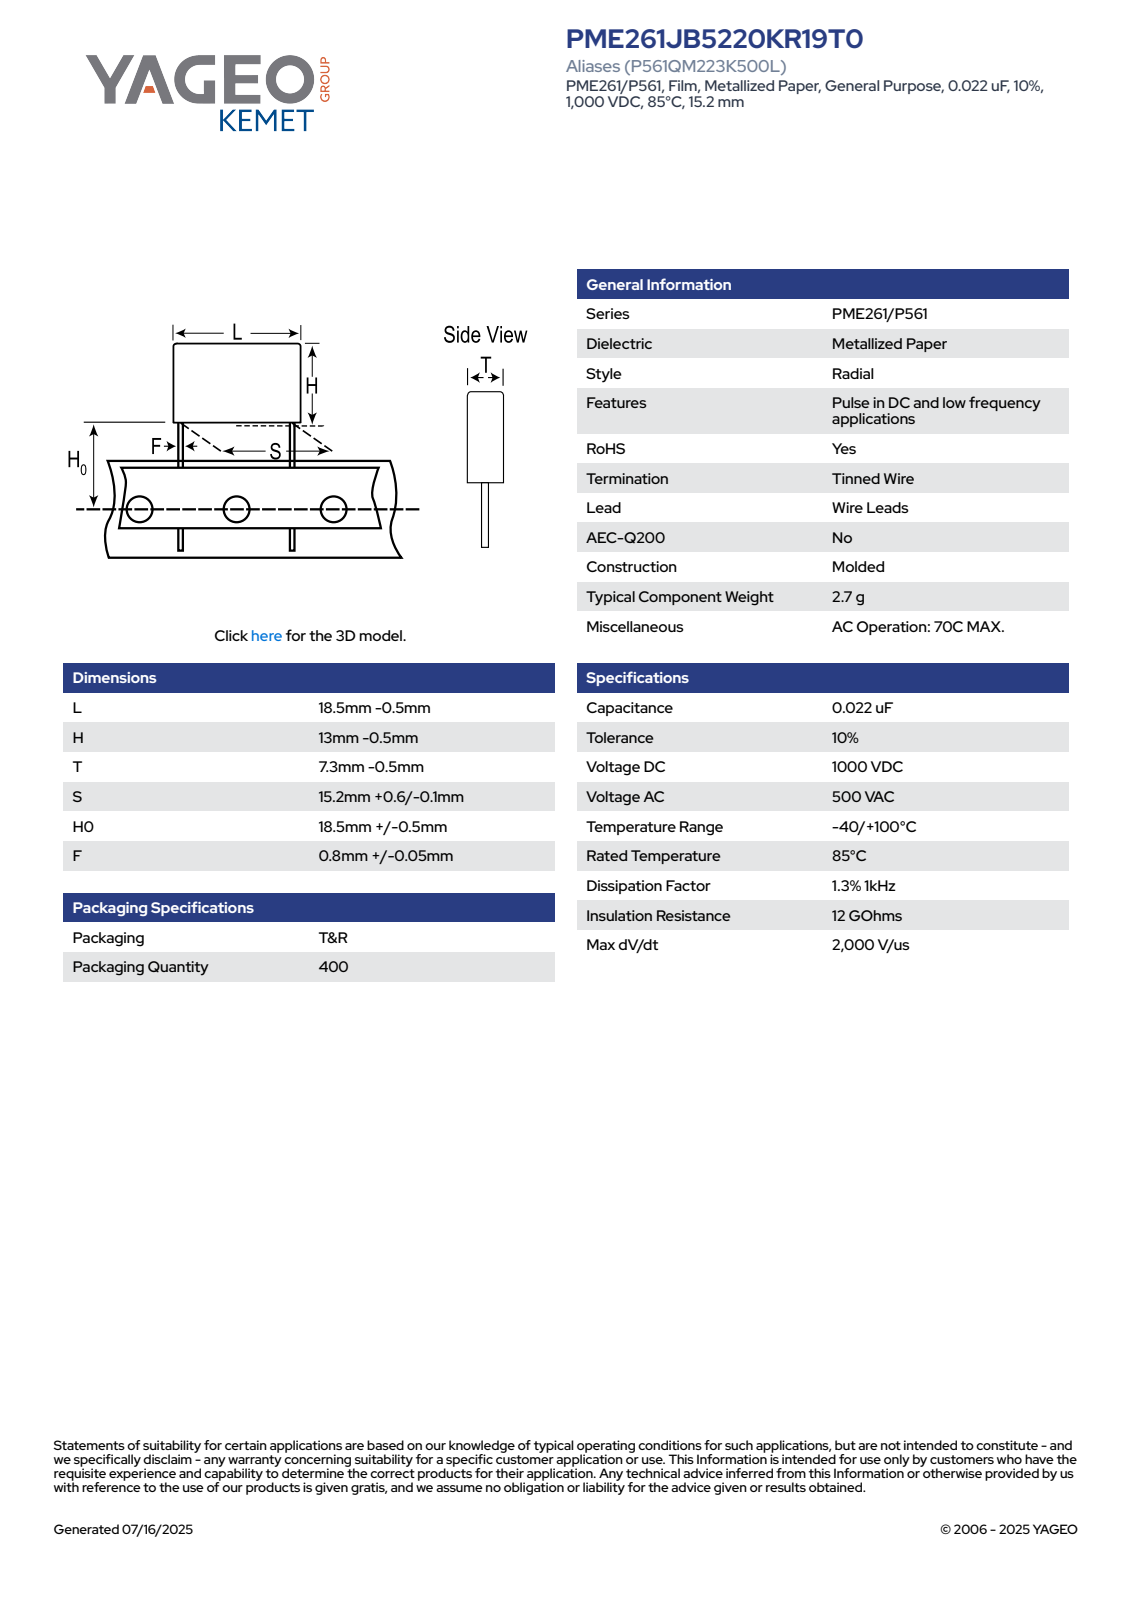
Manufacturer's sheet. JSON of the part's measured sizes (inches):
{"part_name": "CFR_MOLDED_18.5X13X7.3_L18H12.5T6.8S15.2H019F0.85", "step_written_by": "SolidWorks 2014 (AUTOMOTIVE_DESIGN)", "units": "inches", "bodies": {"solids": 4, "faces": 73, "planar": 65, "cylindrical": 8, "other": 0}, "overall_size": [1.24, 0.709, 0.268], "volume_in3": 0.095, "surface_area_in2": 1.51, "round_bosses_or_shafts": [[0.033, 2]], "partial_cylinders_radius": [[0.02, 4]], "face_to_face_distances": [0.268, 0.492, 0.709, 0.748, 1.24, 1.018, 0.27, 0.222, 0.954, 0.206]}
